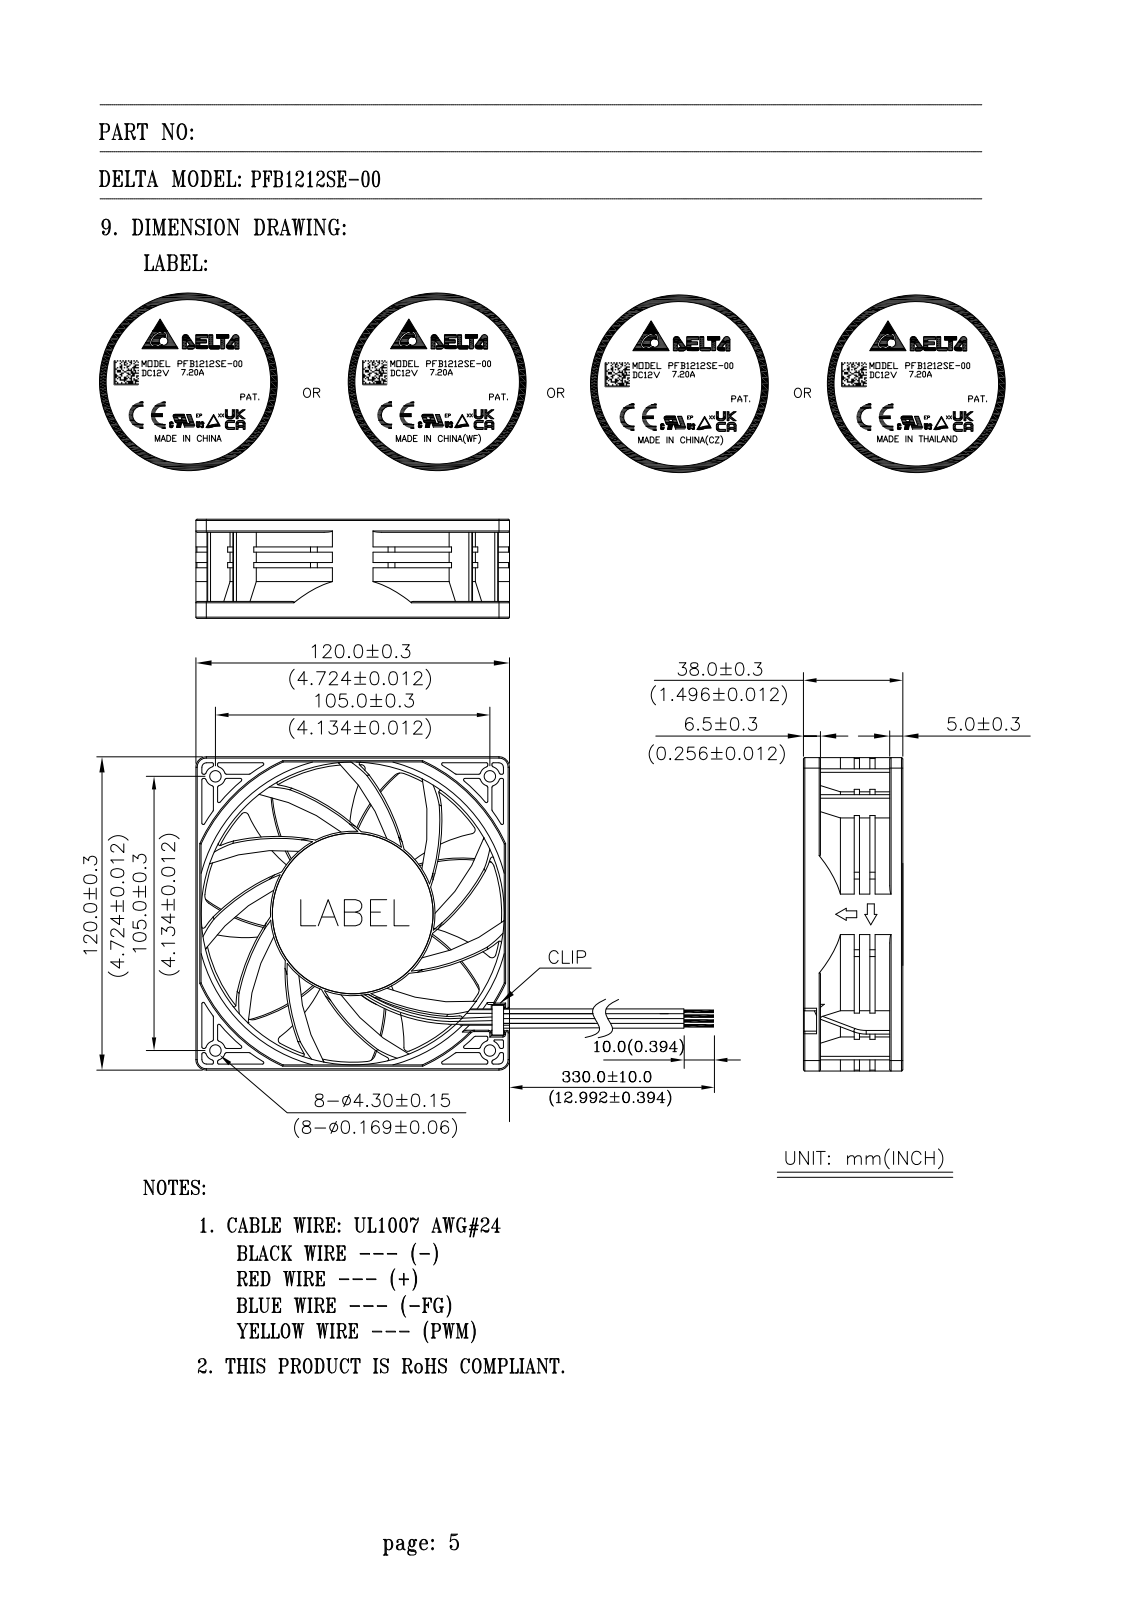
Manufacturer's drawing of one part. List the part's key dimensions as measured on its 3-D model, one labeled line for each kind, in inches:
Part name (STEP PRODUCT): PFB1212SE-00
STEP written by: CREO PARAMETRIC BY PTC INC, 2015080 (CONFIG_CONTROL_DESIGN)
Units: inches
Bodies: 1 solid, 906 faces (462 planar, 379 cylindrical, 65 other)
Overall size (bounding box): 4.724 × 4.724 × 1.496
Volume: 28.35 in³ · Surface area: 100.2 in²
Round holes (diameter × count): ⌀0.173 ×4
Round bosses / shafts (diameter × count): ⌀4.764 ×1, ⌀0.097 ×1
Partial cylindrical surfaces — rounded edges, fillets, slot ends (radius × count): R0.02 ×124, R0.031 ×9, R0.394 ×8, R0.039 ×4, R0.067 ×4, R0.152 ×4, R0.157 ×4, R0.012 ×3
Main face-to-face distances: 1.496, 4.724, 1.299, 0.197, 0.079, 0.063, 0.551, 0.256, 1.043, 1.24
Hole centre spacings: 4.134, 5.846
